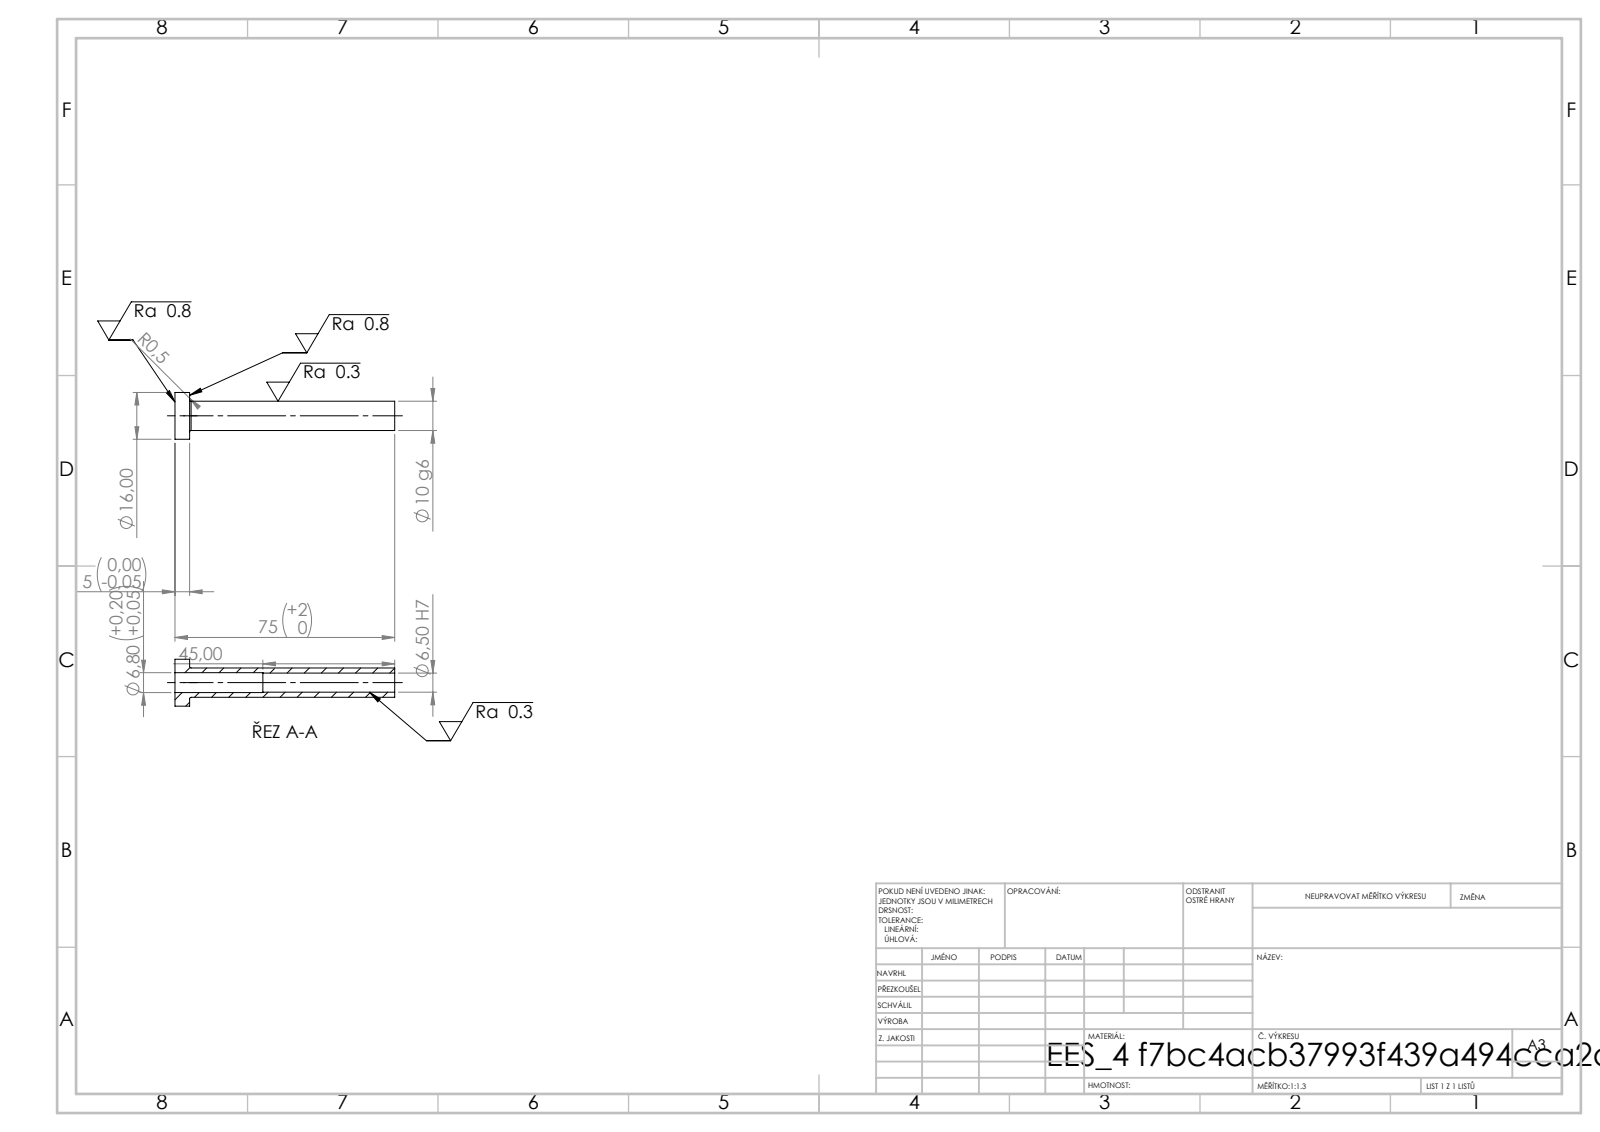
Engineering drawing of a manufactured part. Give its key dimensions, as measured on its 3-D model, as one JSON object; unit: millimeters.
{"step_written_by": "SolidWorks 2019 (CONFIG_CONTROL_DESIGN)", "units": "millimeters", "bodies": {"solids": 1, "faces": 14, "planar": 4, "cylindrical": 8, "other": 2}, "overall_size": [75, 16, 16], "volume_mm3": 3922, "surface_area_mm2": 4339, "round_holes": [[6.5, 1], [6.8, 1]], "round_bosses_or_shafts": [[16, 1], [10, 1]], "face_to_face_distances": [5, 75, 70, 30, 25, 45]}
